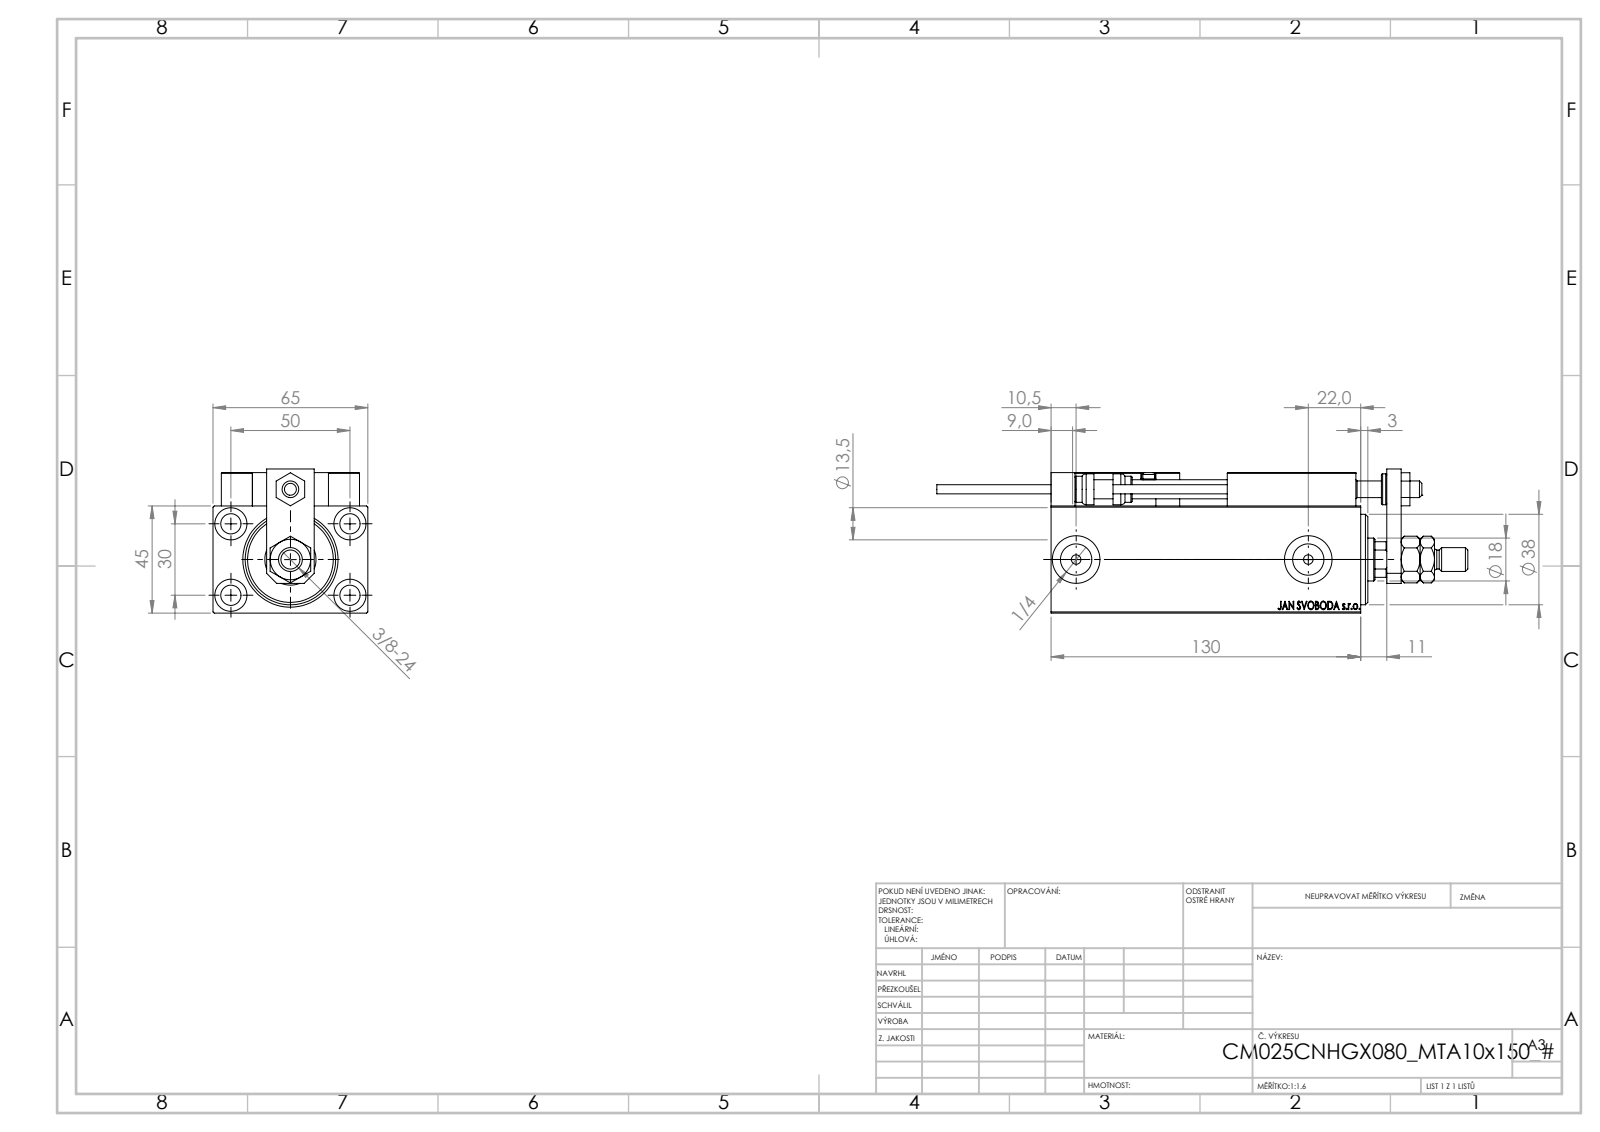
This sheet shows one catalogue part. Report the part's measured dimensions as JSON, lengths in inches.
{"part_name": "ALLEN BOLT D8; ZARAZKA; NUT_D12; SWITCH DIM B,W (+8 more)", "step_written_by": "SolidWorks 2019 (CONFIG_CONTROL_DESIGN)", "units": "inches", "bodies": {"solids": 24, "faces": 1331, "planar": 575, "cylindrical": 192, "other": 564}, "overall_size": [8.78, 2.559, 2.382], "volume_in3": 23.08, "surface_area_in2": 157.6, "round_holes": [[0.157, 6], [0.315, 5], [0.335, 5], [0.126, 4], [0.531, 4], [0.197, 2], [0.518, 2], [0.787, 2], [0.276, 1], [0.571, 1], [0.709, 1], [0.846, 1]], "round_bosses_or_shafts": [[0.197, 2], [0.15, 2], [0.512, 1], [0.433, 1], [0.394, 1], [0.315, 1]], "partial_cylinders_radius": [[0.012, 30], [0.118, 2], [0.335, 1]], "face_to_face_distances": [1.772, 2.559, 0.551, 0.236, 2.323, 0.118, 0.512, 0.787, 5.551, 0.138], "hole_center_spacings": [1.148, 0.448, 0.787, 1.138, 1.165, 1.169, 1.181, 1.42]}
